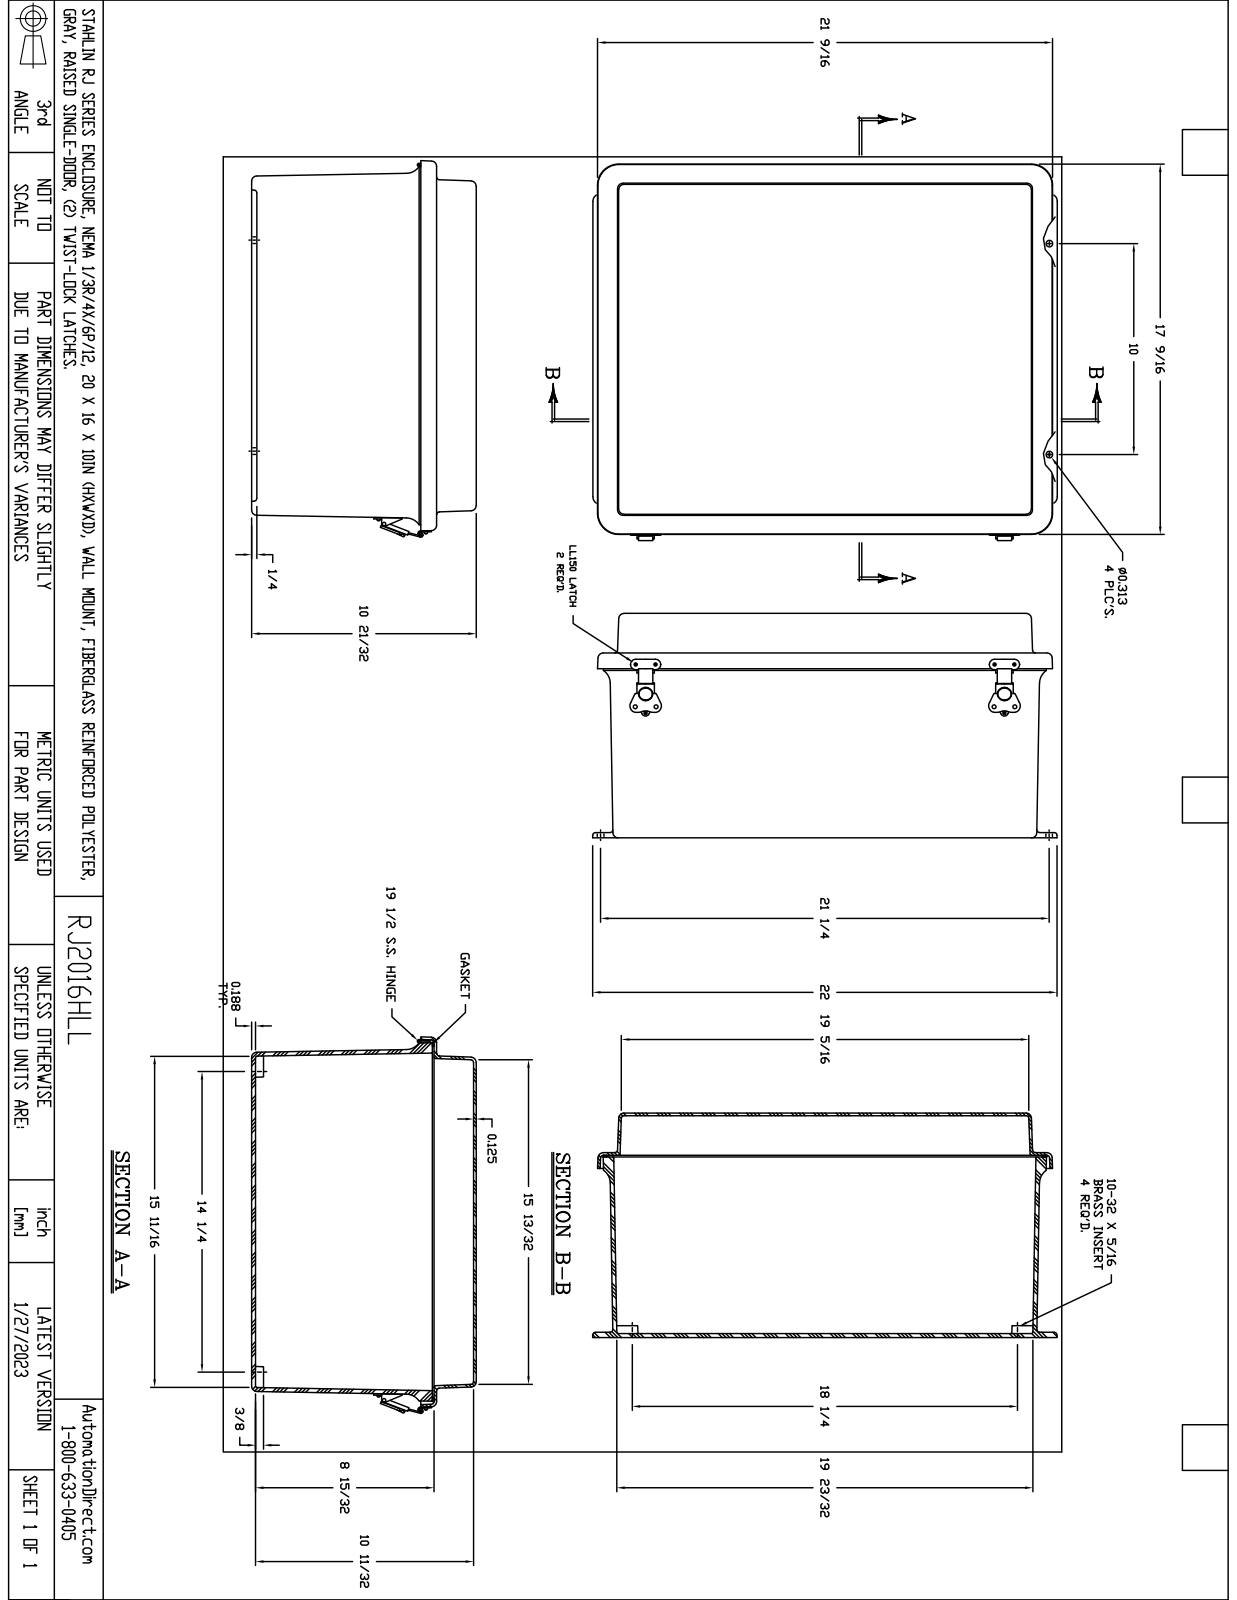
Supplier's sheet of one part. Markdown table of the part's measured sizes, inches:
| quantity | value |
| --- | --- |
| part name | MR2016HLL |
| STEP written by | SolidWorks 2018 (AUTOMOTIVE_DESIGN) |
| units | inches |
| bodies | 52 solids, 1357 faces (645 planar, 513 cylindrical, 199 other) |
| overall size | 22 × 17.753 × 10.642 |
| volume | 270.5 in³ |
| surface area | 3 193 in² |
| round holes (diameter × count) | 0.104 × 20, 0.14 × 20, 0.131 × 12, 0.152 × 5, 0.13 × 4, 0.156 × 4, 0.165 × 4, 0.197 × 4, 0.218 × 4, 0.118 × 2, 0.138 × 2, 0.181 × 2 |
| round bosses / shafts (diameter × count) | 0.14 × 20, 0.27 × 4, 0.583 × 2, 0.524 × 2, 0.209 × 2, 0.185 × 2, 0.128 × 2, 0.155 × 1 |
| partial cylindrical surfaces (radius × count) | 0.125 × 22, 0.079 × 19, 0.25 × 12, 0.039 × 8, 0.045 × 8, 0.047 × 8, 0.086 × 8, 0.092 × 8 |
| main face-to-face distances | 0.187, 0.125, 0.188, 10.517, 10.329, 10.642, 10.454, 2, 8.642, 8.454 |
| hole center spacings | 3.75, 7.5, 17, 11, 11.5, 7.25, 7.75, 0.945 |
